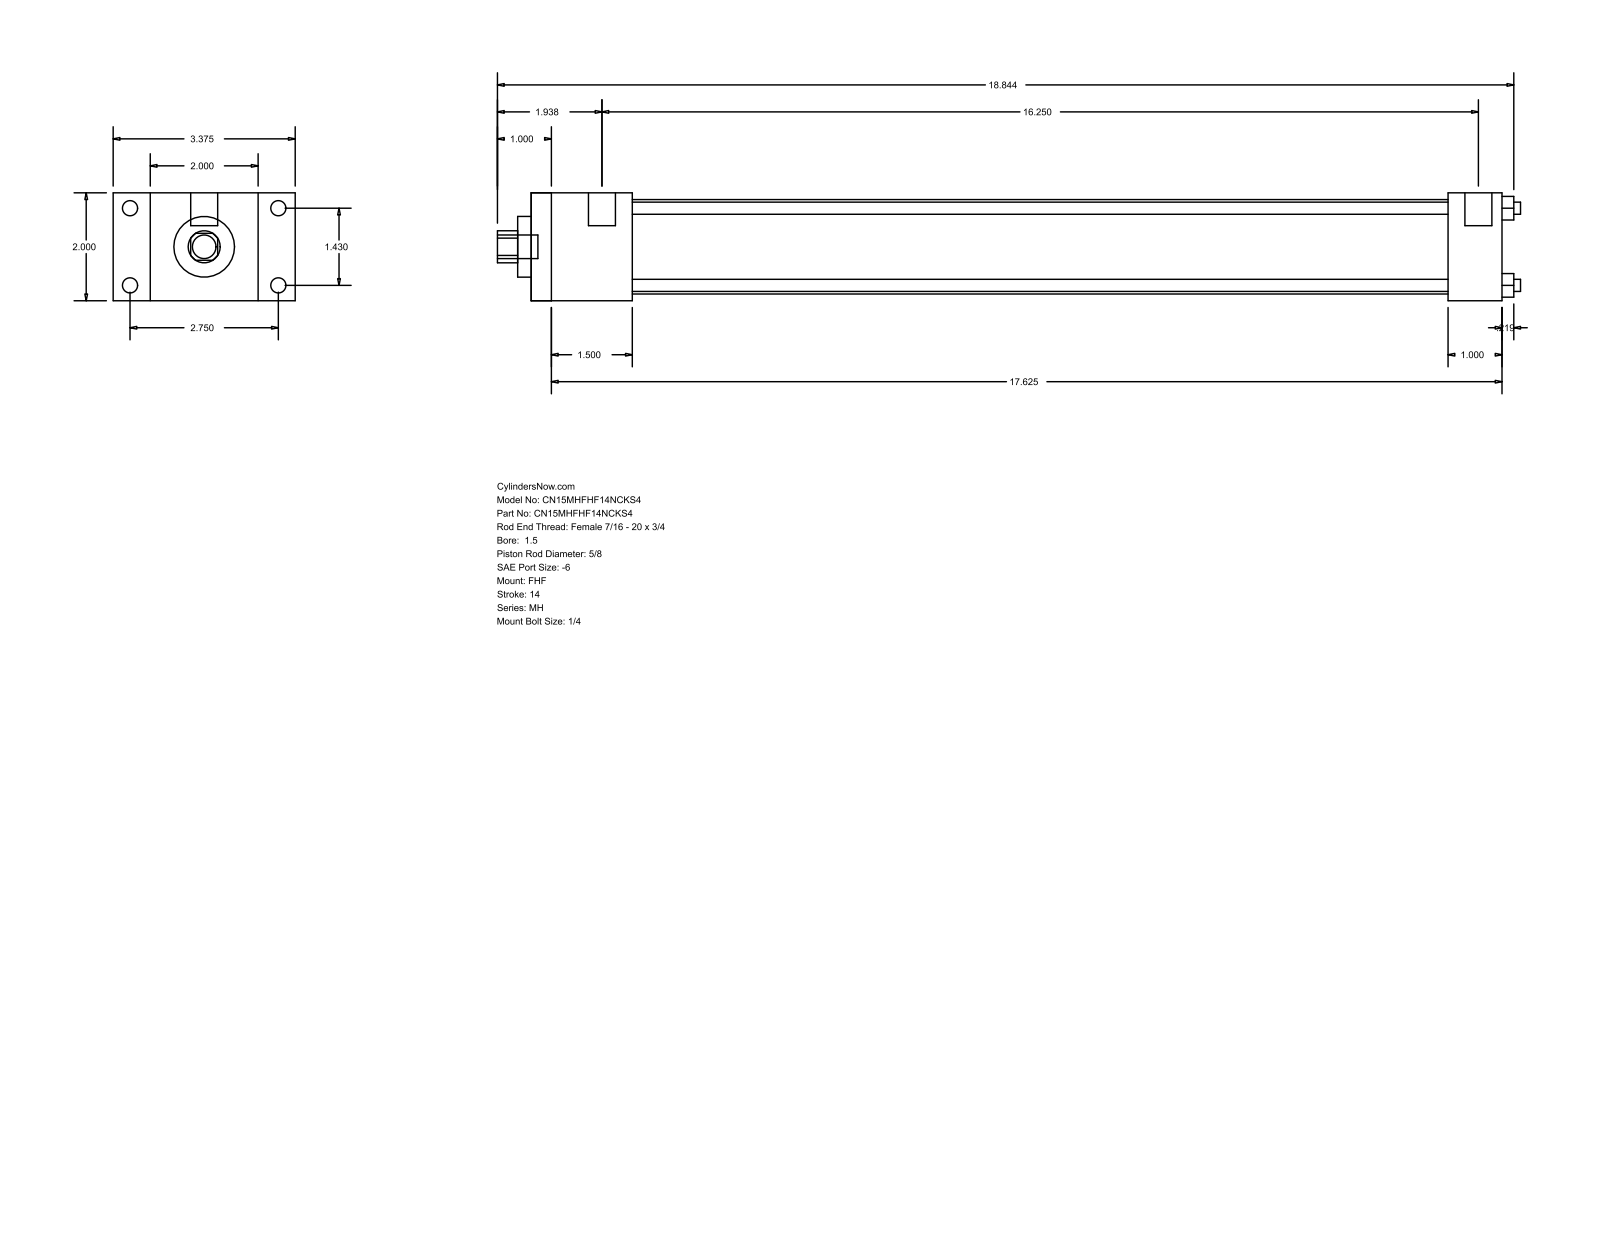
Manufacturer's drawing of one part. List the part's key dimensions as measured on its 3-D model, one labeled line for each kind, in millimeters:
Part name (STEP PRODUCT): MH_FHF__0150_0.625
STEP written by: GSSL Pune (CONFIG_CONTROL_DESIGN)
Units: millimetres
Bodies: 0 solids, 88 faces (60 planar, 28 cylindrical, 0 other)
Overall size (bounding box): 481.81 × 85.72 × 50.8
Round holes (diameter × count): ⌀5.71 ×4, ⌀15.88 ×1, ⌀28.57 ×1, ⌀44.45 ×1
Round bosses / shafts (diameter × count): ⌀7.14 ×4, ⌀5.56 ×4, ⌀12.7 ×2, ⌀11.11 ×1
Partial cylindrical surfaces — rounded edges, fillets, slot ends (radius × count): R7.54 ×1
Main face-to-face distances: 50.8, 17.46, 68.26, 47.62, 85.72, 457.19, 409.57, 431.8, 384.18, 25.39
Hole centre spacings: 25.68, 36.32, 51.36
